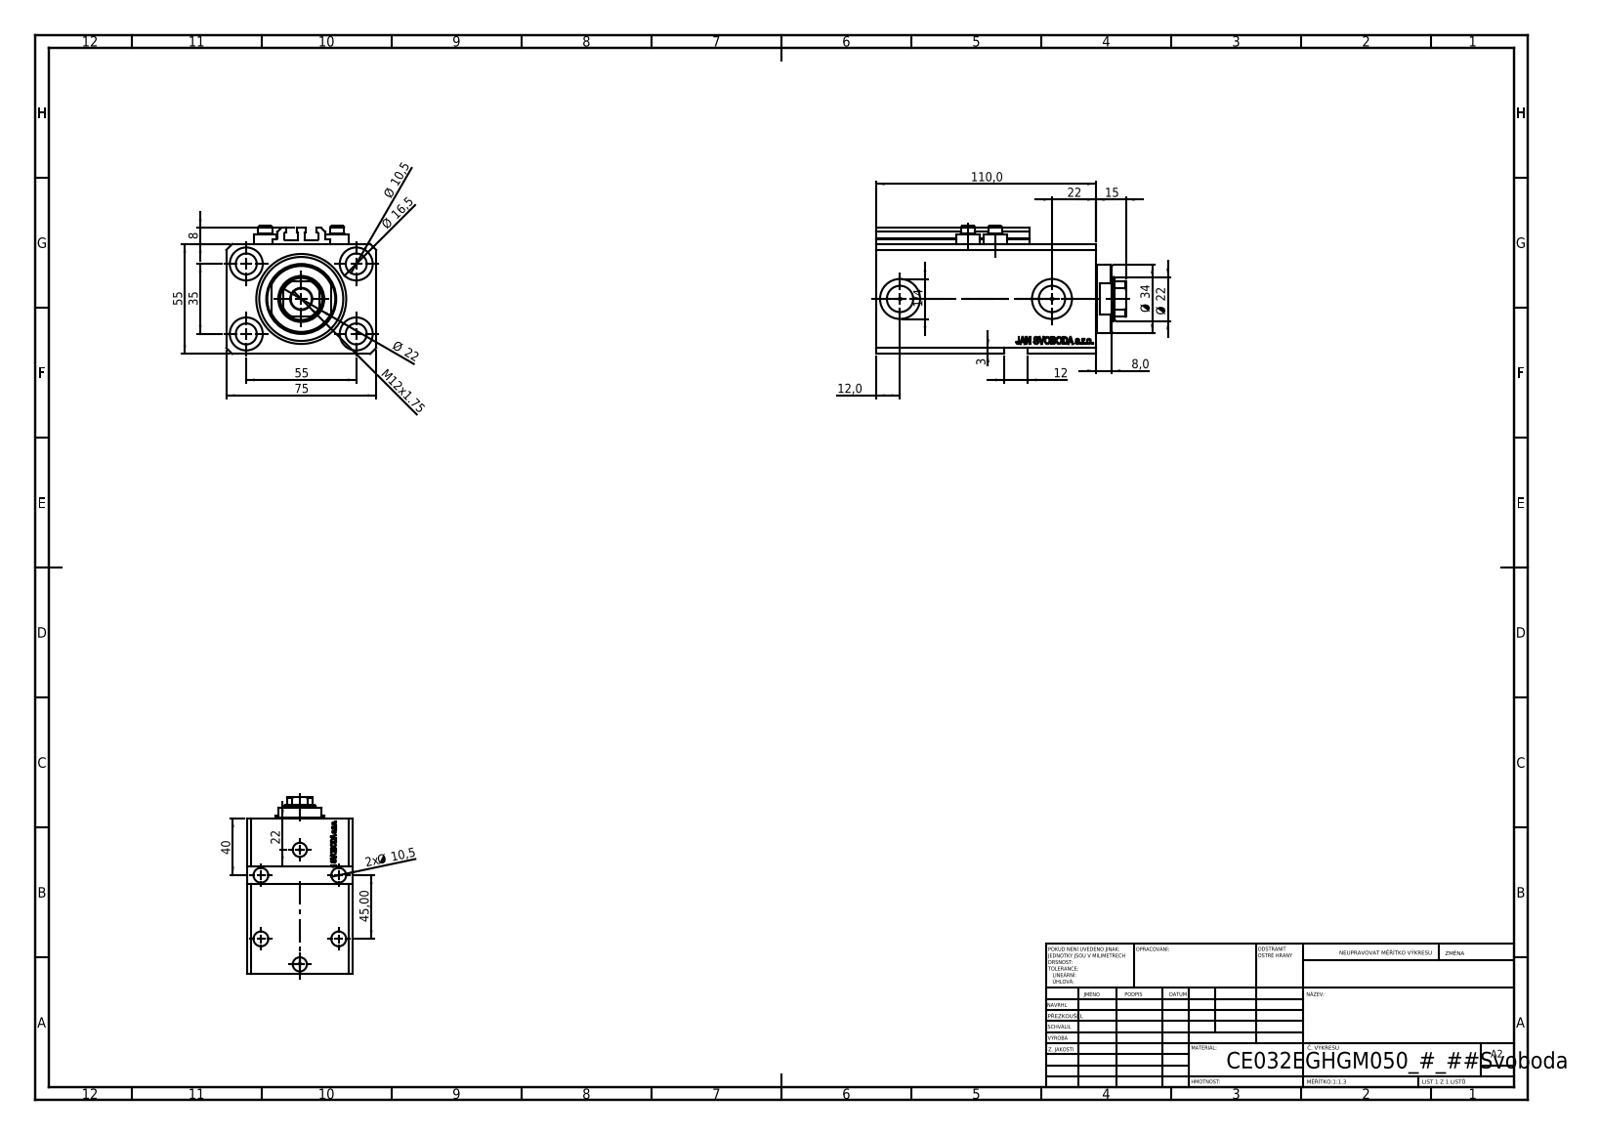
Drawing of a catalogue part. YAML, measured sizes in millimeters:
part_name: "V250CE_C_VCP; ALLEN BOLT V250CE; V250CE_E_Body; V250CE_VC_E"
step_written_by: "SolidWorks 2019 (CONFIG_CONTROL_DESIGN)"
units: millimeters
bodies: {solids: 8, faces: 1084, planar: 514, cylindrical: 146, other: 424}
overall_size: [125, 75, 64]
volume: 381338
surface_area: 95642
round_holes:
  - {diameter: 10.5, count: 9}
  - {diameter: 1.25, count: 4}
  - {diameter: 4, count: 4}
  - {diameter: 16.5, count: 4}
  - {diameter: 10, count: 2}
  - {diameter: 13.16, count: 2}
  - {diameter: 20, count: 2}
  - {diameter: 22, count: 1}
  - {diameter: 32, count: 1}
  - {diameter: 45, count: 1}
round_bosses_or_shafts:
  - {diameter: 11.6, count: 4}
  - {diameter: 7, count: 4}
  - {diameter: 34, count: 1}
partial_cylinders:
  - {radius: 0.2, count: 10}
  - {radius: 10.5, count: 1}
face_to_face_distances: [55, 75, 15, 110, 95, 3, 9.9, 85.1, 100.1, 57]
hole_center_spacings: [32.6, 32.87, 55, 68.74, 13.6, 14.09, 23.05, 25.81]
